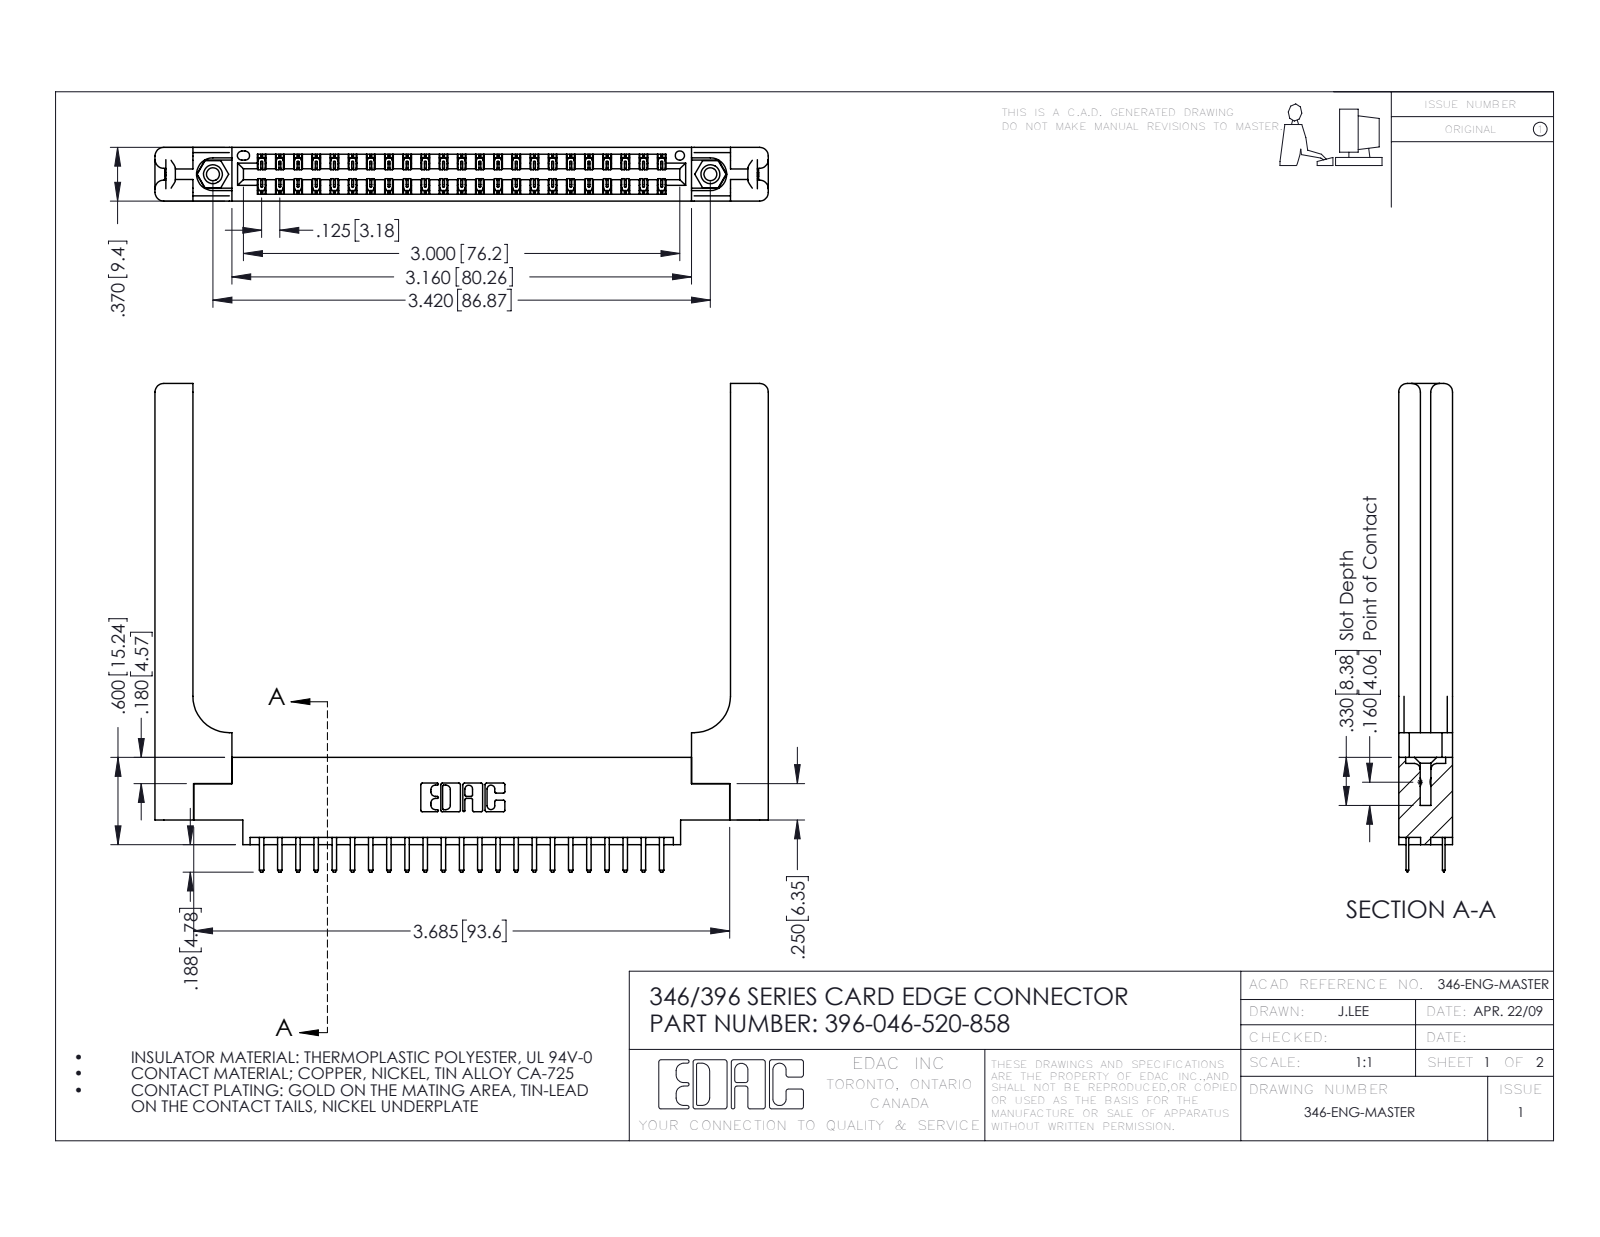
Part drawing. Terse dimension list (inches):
name: 345-250-001_345-250-001-102; 345-292-001_345-293-120; 346-220-058_345-220-058; 346 Part_0.170 Offset - 0.156 Dia-TH (+1 more)
written by: SolidWorks 2016 (CONFIG_CONTROL_DESIGN)
unit: in
bodies: 51 solids, 2958 faces (1930 planar, 968 cylindrical, 60 other)
size: 4.216 × 3.358 × 0.37
volume: 1.075 in³; area: 29.01 in²
holes: 2× ⌀0.089, 2× ⌀0.125, 2× ⌀0.156, 1× ⌀0.064
bosses: 2× ⌀0.155
rounds: 69× R0.006, 50× R0.01, 22× R0.01, 16× R0.06, 6× R0.007, 6× R0.031, 3× R0.026, 2× R0.014
face distances: 0.37, 0.072, 0.048, 0.322, 0.148, 0.15, 0.25, 0.298, 0.025, 0.077
hole spacings: 0.246, 3.212, 3.42
